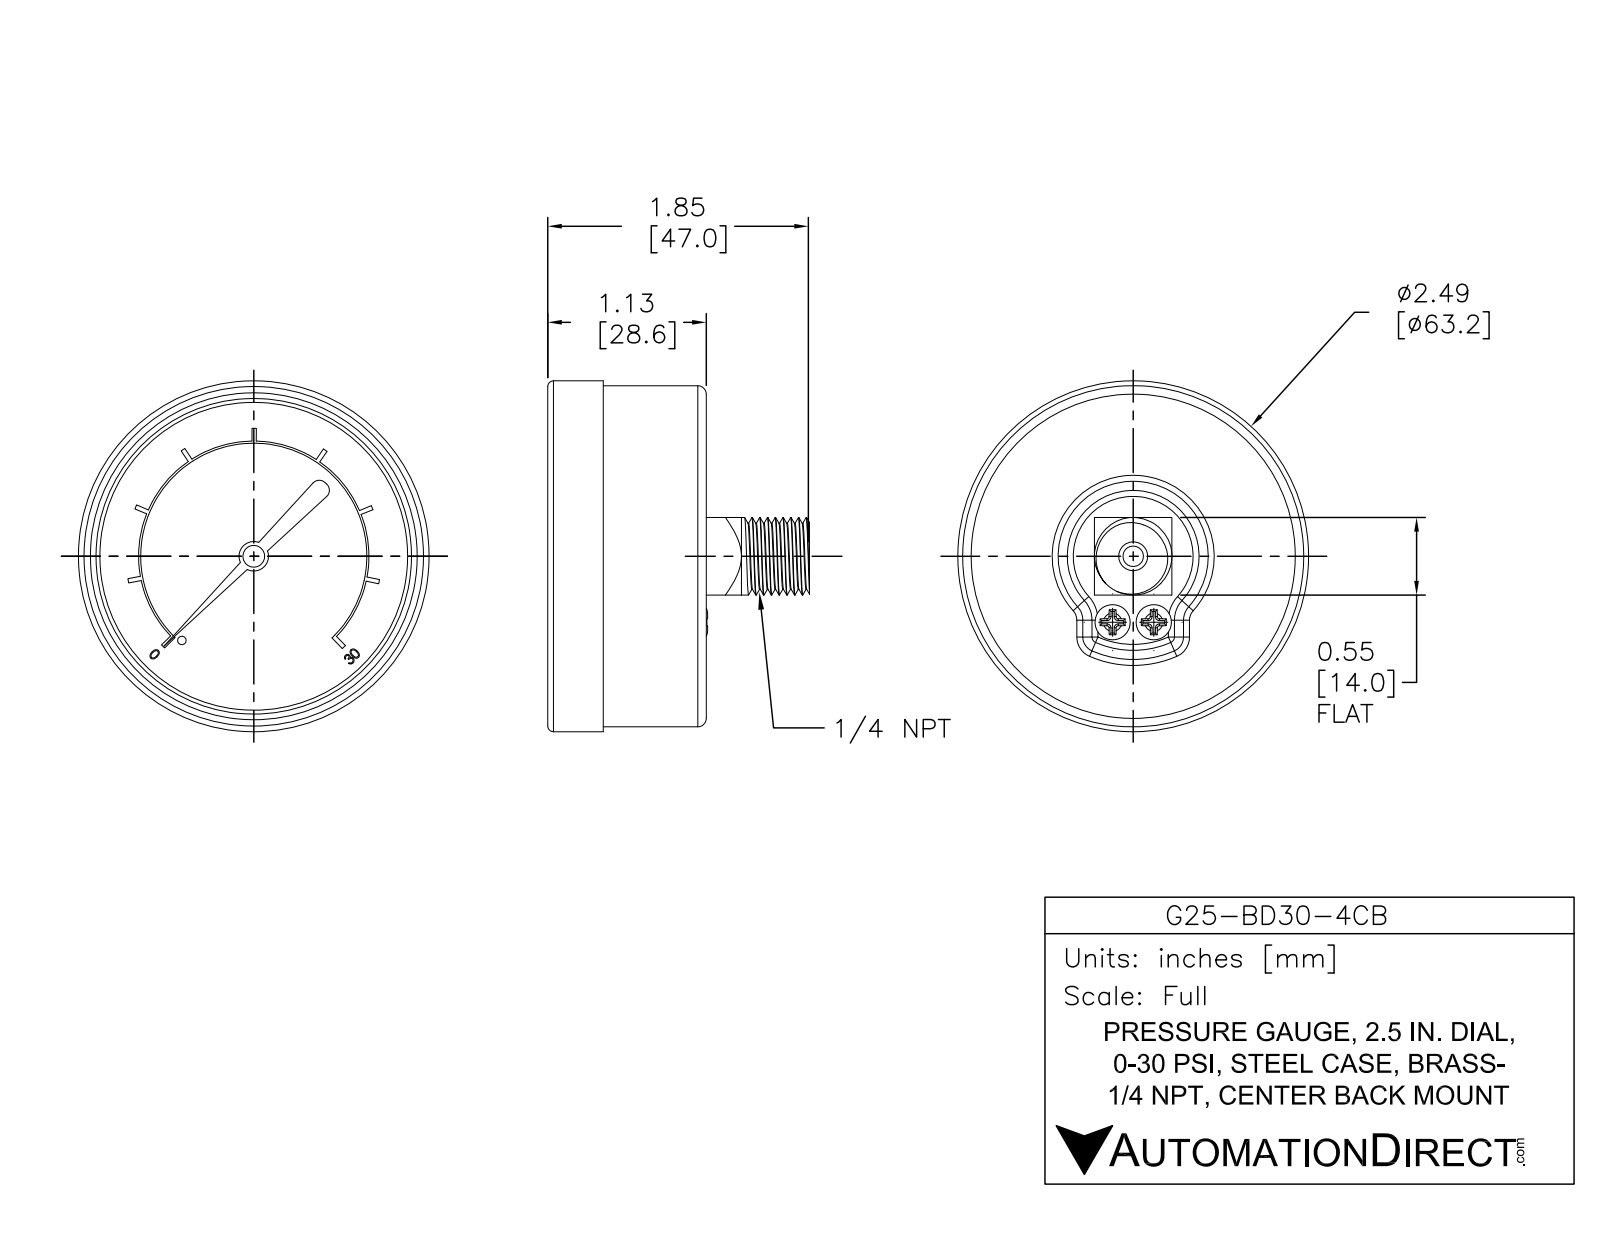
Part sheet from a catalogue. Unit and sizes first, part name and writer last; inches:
Units: inches
Overall size (bounding box): 2.49 × 2.49 × 1.858
Round holes (diameter × count): ⌀0.145 ×1, ⌀2.185 ×1
Round bosses / shafts (diameter × count): ⌀0.25 ×2, ⌀2.49 ×1, ⌀2.421 ×1, ⌀0.55 ×1, ⌀0.178 ×1, ⌀0.099 ×1, ⌀0.04 ×1
Partial cylindrical surfaces — rounded edges, fillets, slot ends (radius × count): R0.06 ×4, R0.03 ×2, R0.115 ×1, R0.813 ×1, R0.823 ×1
Main face-to-face distances: 0.835, 0.1, 1.125, 0.29, 0.735, 1.025, 0.731, 0.631, 0.104, 0.394
Volume: 4.301 in³ · Surface area: 22.47 in²
Bodies: 1 solid, 199 faces (98 planar, 32 cylindrical, 69 other)
Part name (STEP PRODUCT): G25-BD30-4CB
STEP written by: SolidWorks 2021 (AUTOMOTIVE_DESIGN)
